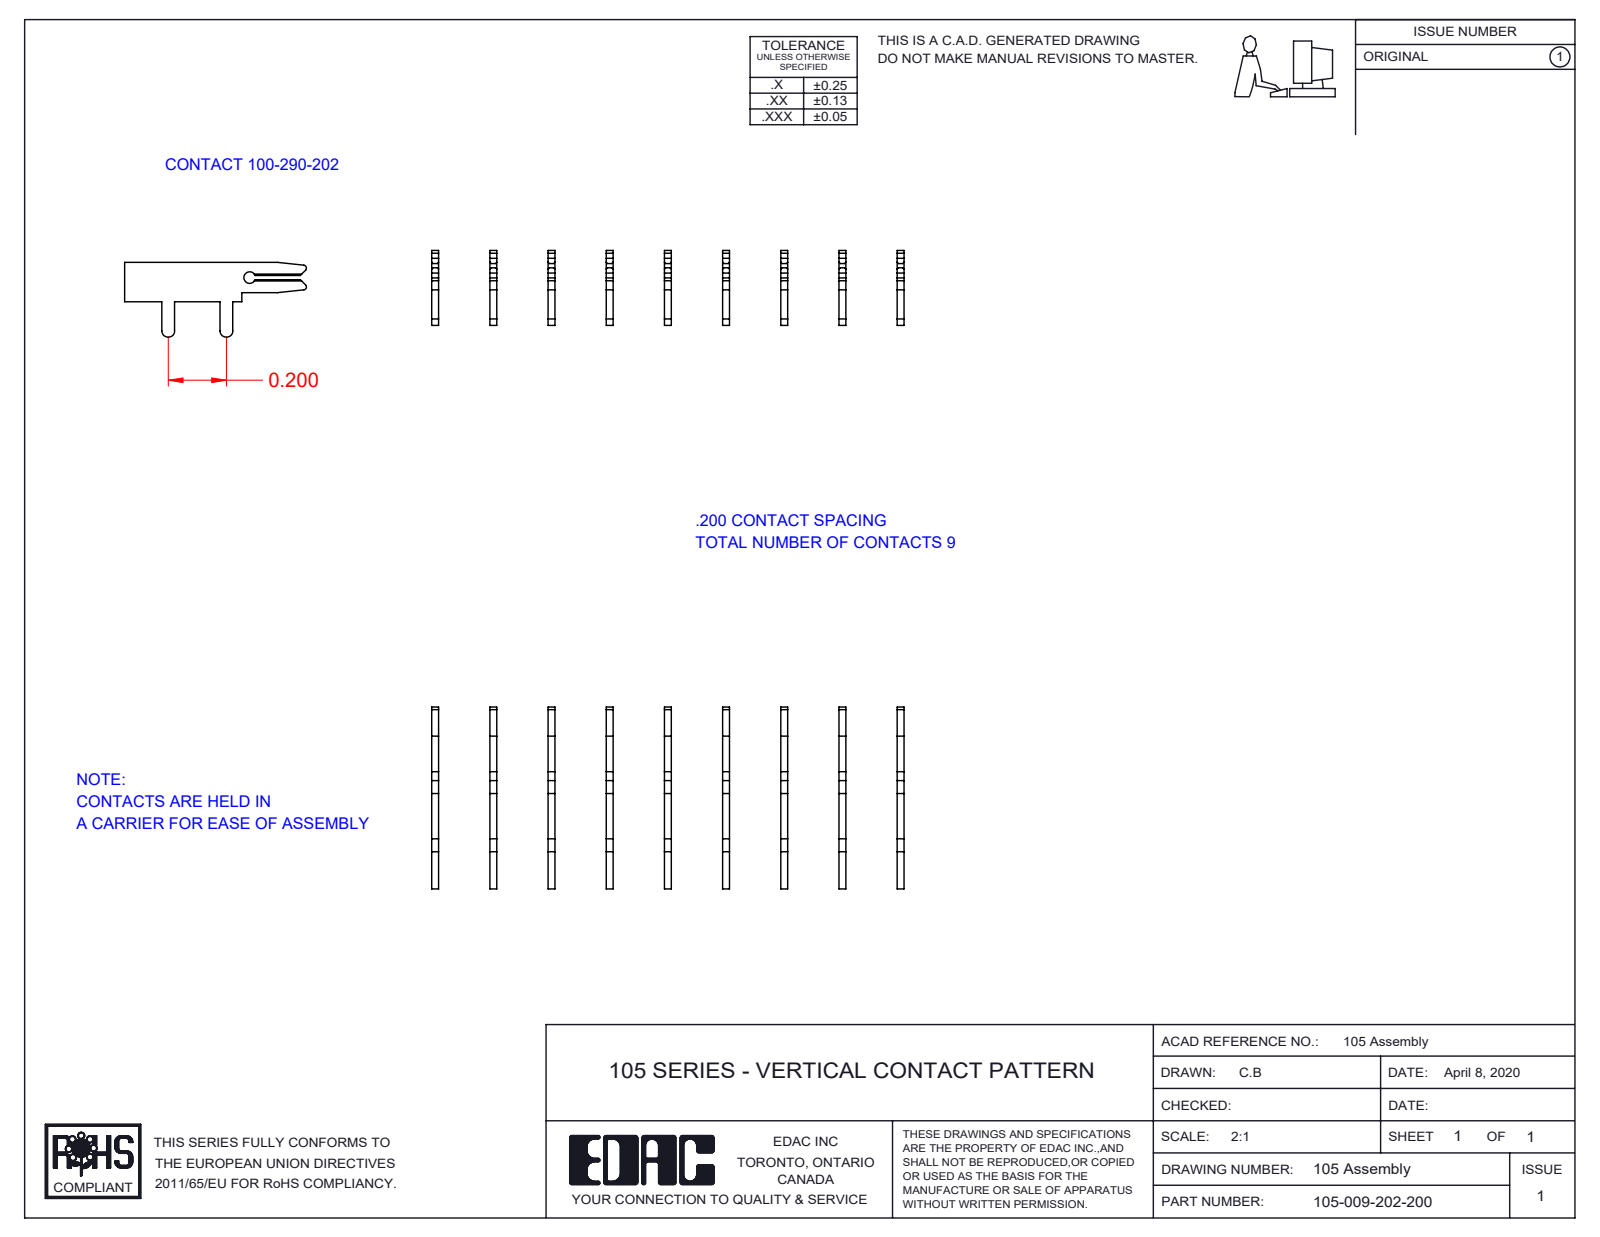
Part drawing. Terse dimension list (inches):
name: 100-290-001_100-290-202; 105-009-202-200
written by: SolidWorks 2016 (CONFIG_CONTROL_DESIGN)
unit: in
bodies: 9 solids, 270 faces (207 planar, 63 cylindrical, 0 other)
size: 1.624 × 0.625 × 0.257
volume: 0.017 in³; area: 1.971 in²
holes: 1× ⌀0.04
rounds: 2× R0.01, 2× R0.022
face distances: 0.2, 0.4, 0.6, 0.8, 0.024, 1, 0.224, 0.176, 0.424, 0.376
